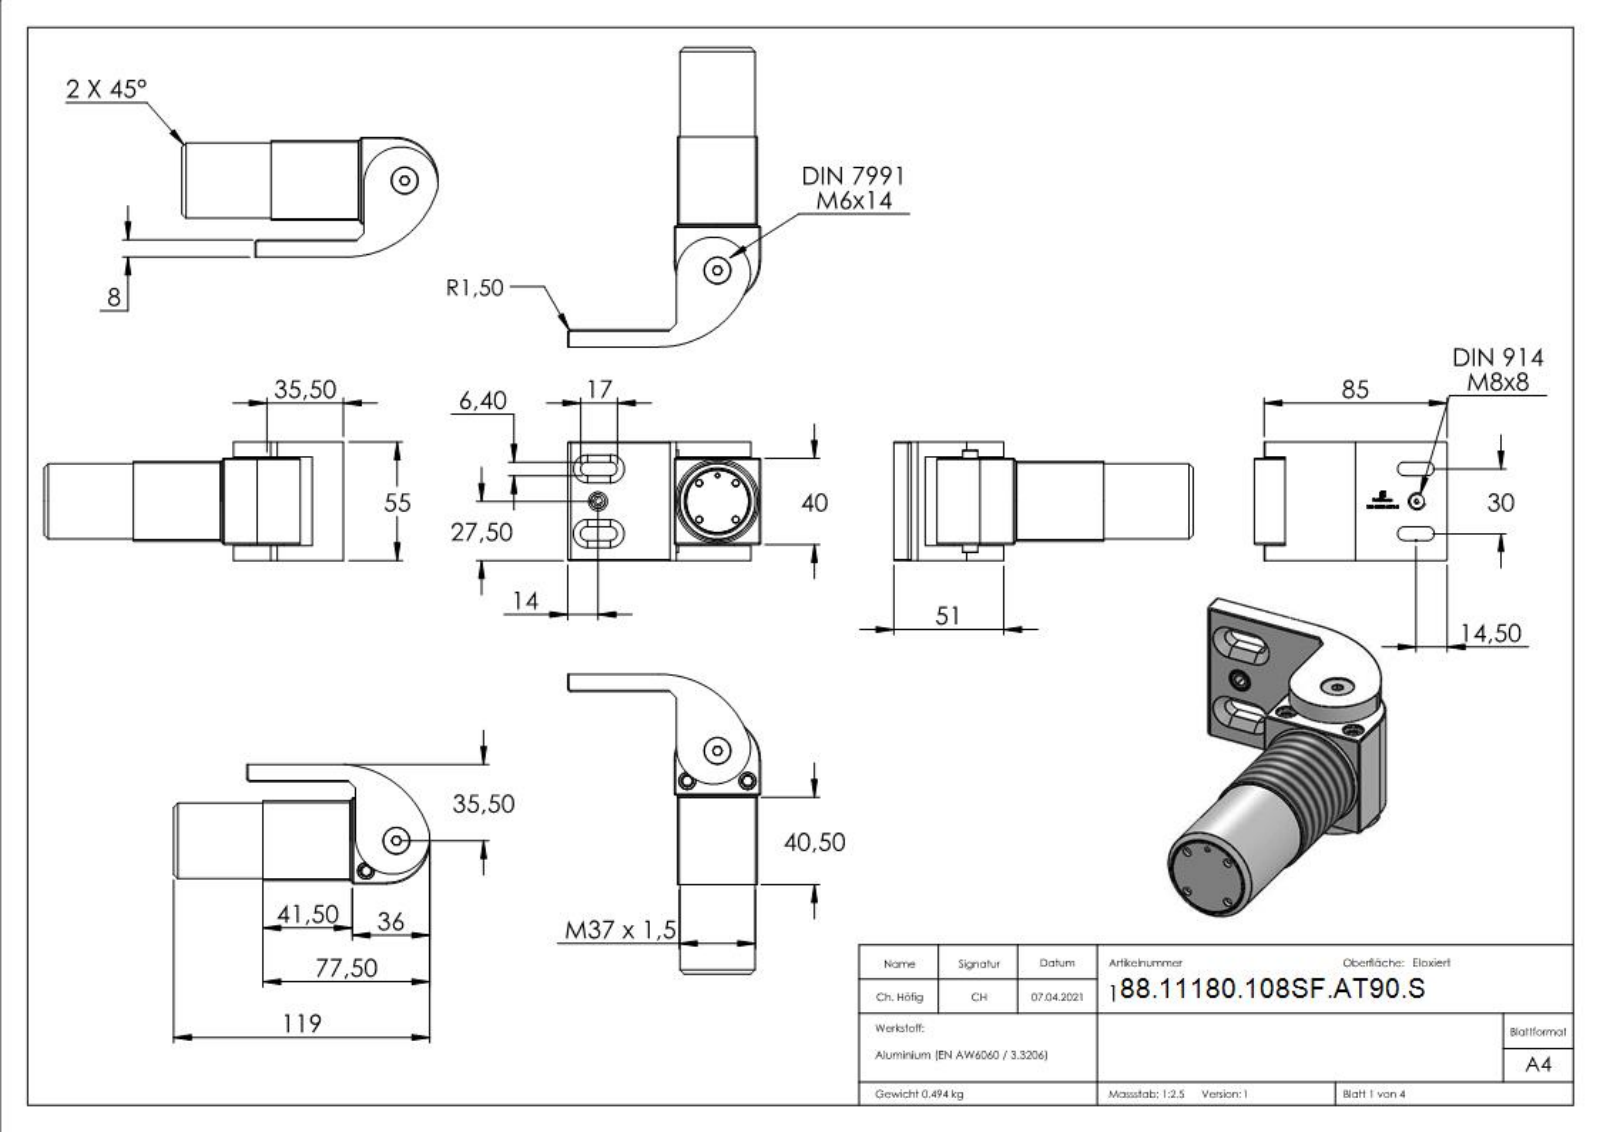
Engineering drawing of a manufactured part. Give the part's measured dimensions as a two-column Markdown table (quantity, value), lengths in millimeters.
| quantity | value |
| --- | --- |
| part name | DIN914; 180-108SF-AT90-S; Teil2; DIN-7991 M3-M10 (+5 more) |
| STEP written by | SolidWorks 2018 (CONFIG_CONTROL_DESIGN) |
| units | millimeters |
| bodies | 7 solids, 672 faces (300 planar, 100 cylindrical, 272 other) |
| overall size | 14000.45 × 5999.86 × 5999.7 |
| volume | 180 640 mm³ |
| surface area | 36 717 mm² |
| round holes (diameter × count) | 3.1 × 4, 8 × 2, 1.9 × 1, 5 × 1, 6.5 × 1, 6.8 × 1, 12.5 × 1, 15.7 × 1, 24 × 1, 29.7 × 1 |
| round bosses / shafts (diameter × count) | 7.8 × 2, 37 × 1, 35 × 1, 29.5 × 1, 26 × 1, 23.6 × 1, 15.5 × 1, 12 × 1 |
| partial cylindrical surfaces (radius × count) | 0.5 × 12, 3.2 × 4, 1.5 × 1, 10 × 1, 17.25 × 1, 20 × 1, 44.11 × 1 |
| main face-to-face distances | 48, 7, 8, 55, 47.5, 7.5, 40.5, 0.5, 40, 14.5 |
| hole center spacings | 12.01, 16.98, 9.19, 19.8, 22.18, 24.01, 47.77, 64.55 |
